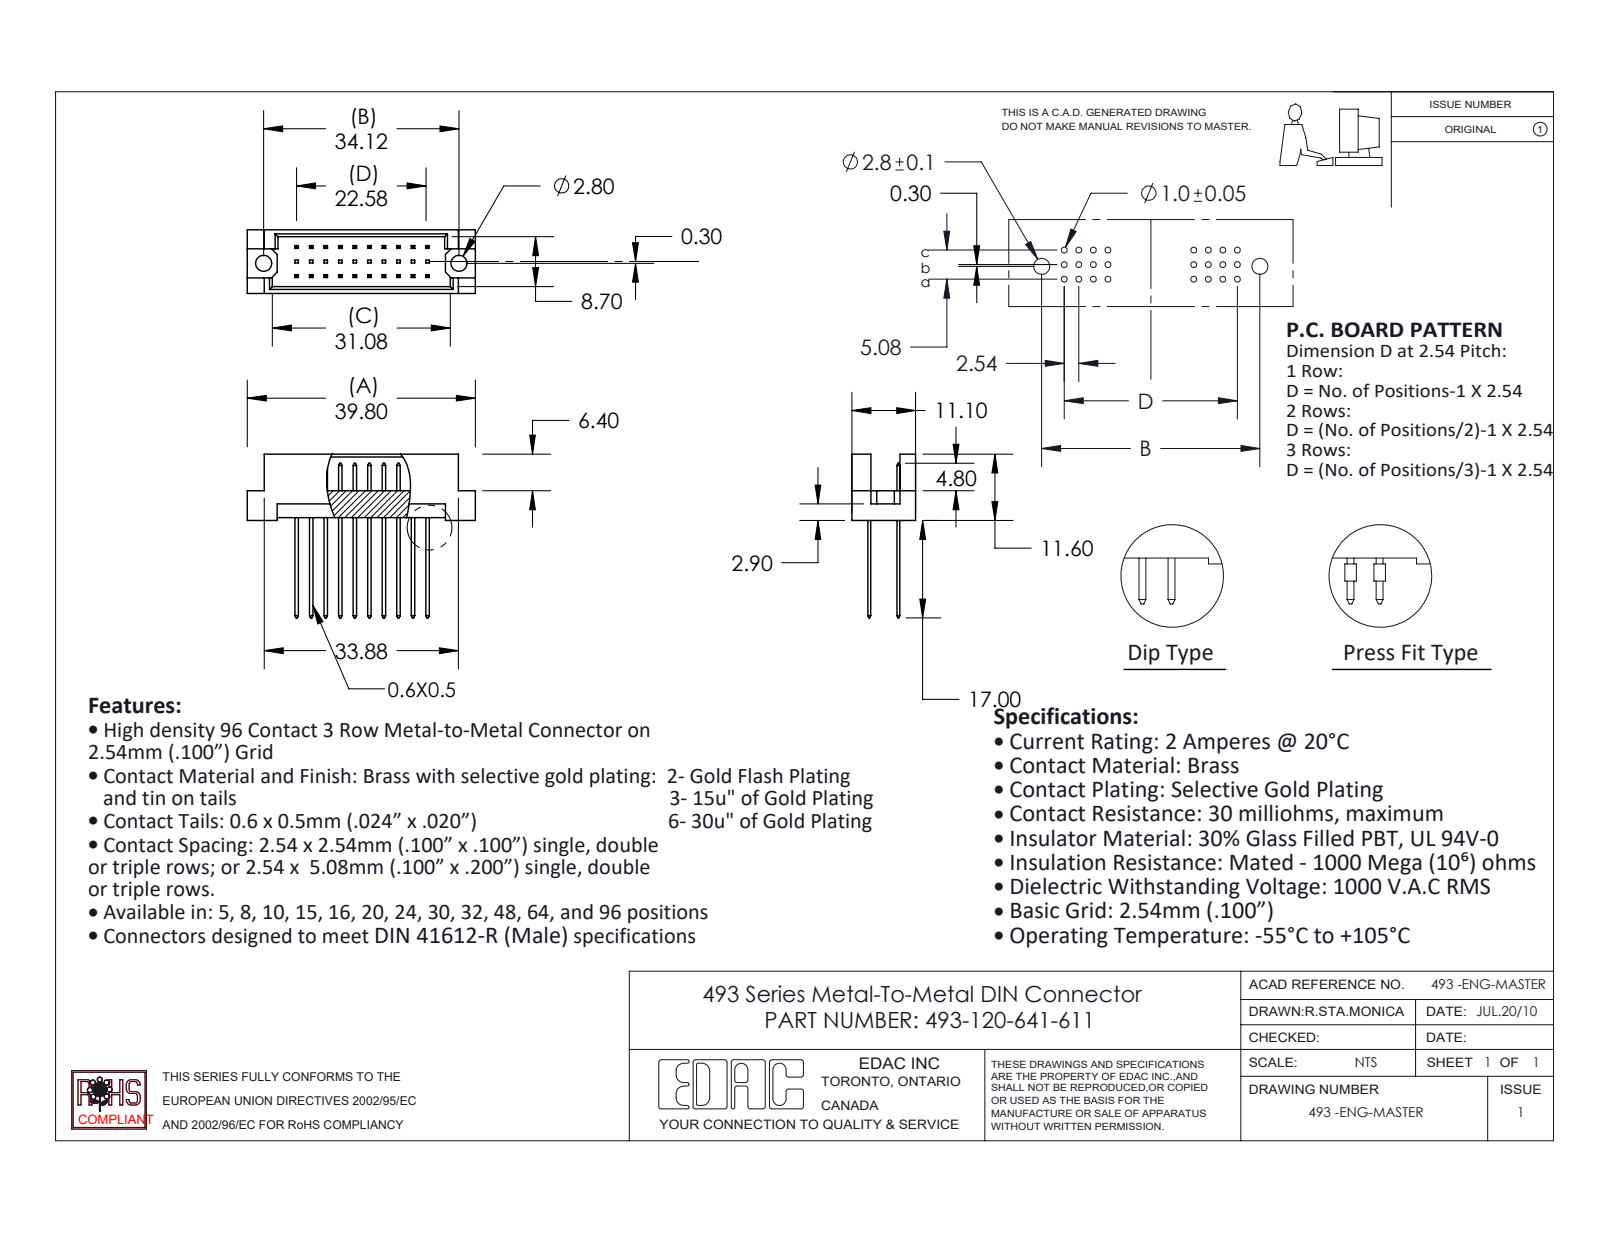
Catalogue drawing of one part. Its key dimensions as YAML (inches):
part_name: "493-120-641-611; 493 Part_30; 493-290_41"
step_written_by: "SolidWorks 2020 (CONFIG_CONTROL_DESIGN)"
units: inches
bodies: {solids: 21, faces: 452, planar: 448, cylindrical: 4, other: 0}
overall_size: [1.567, 1.126, 0.437]
volume: 0.155
surface_area: 6.073
round_holes:
  - {diameter: 0.11, count: 2}
face_to_face_distances: [0.2, 0.1, 0.02, 0.047, 0.39, 0.437, 0.109, 0.128, 0.309, 0.328]
hole_center_spacings: [1.343]
